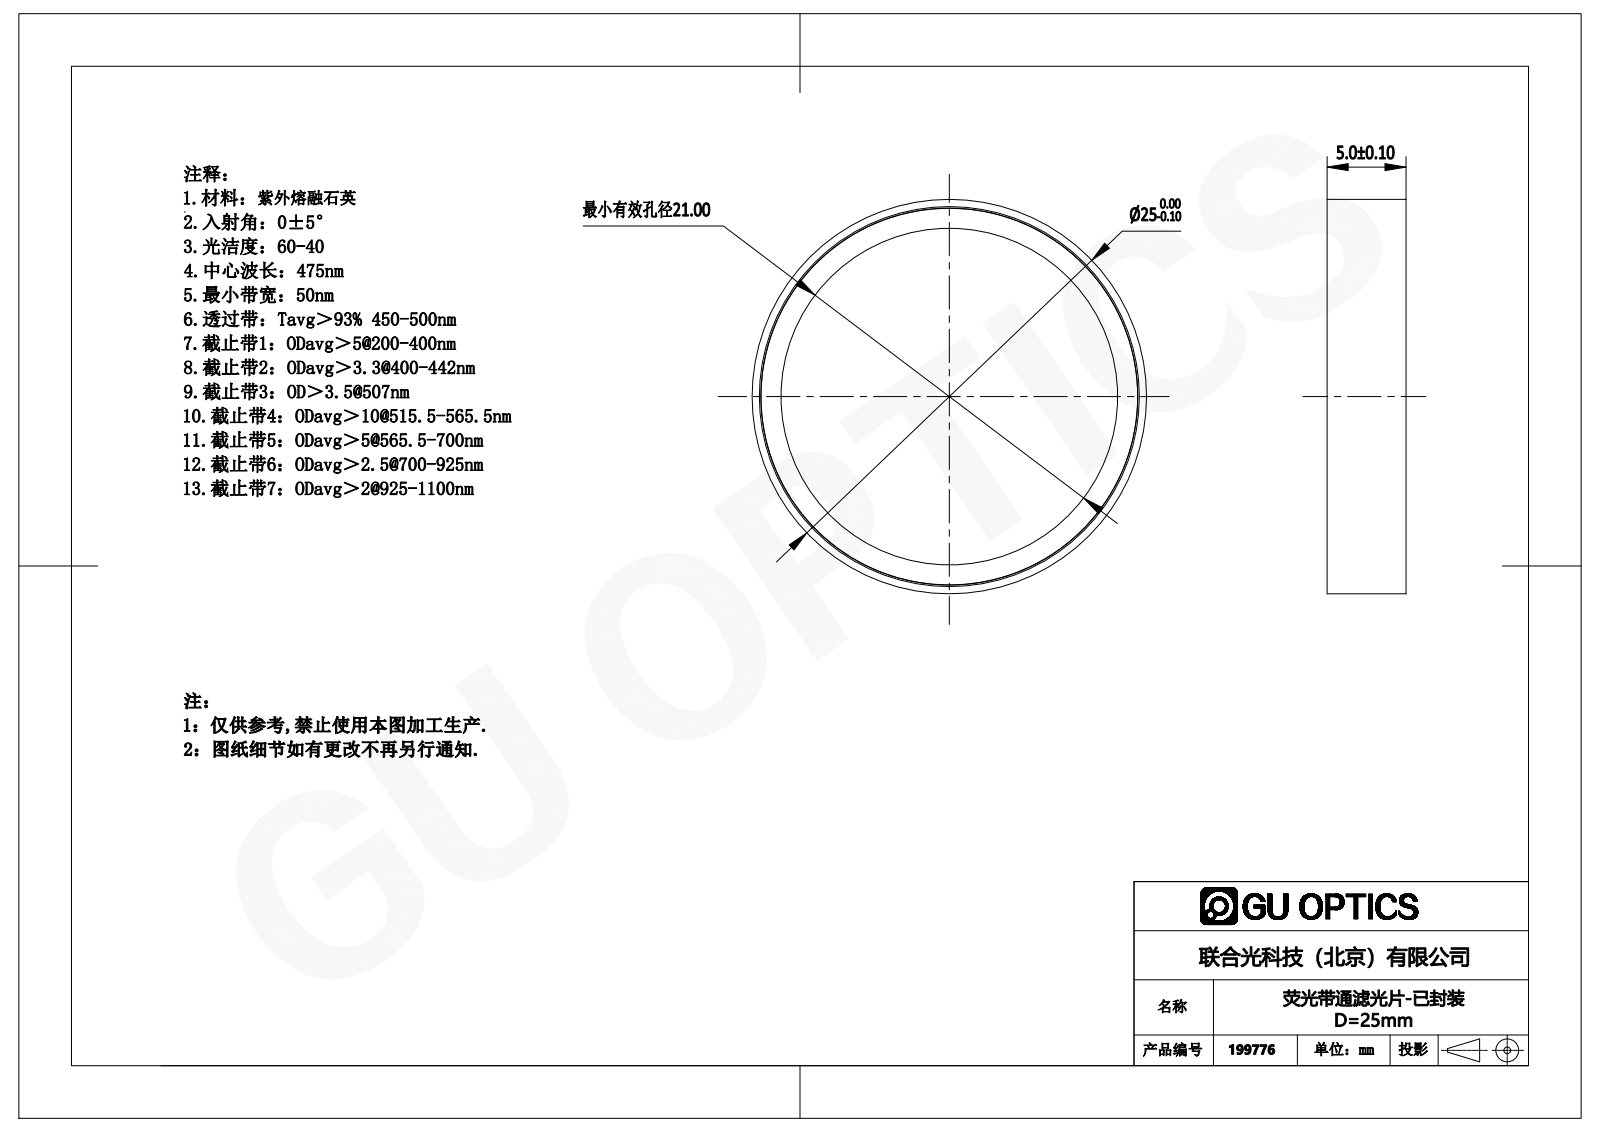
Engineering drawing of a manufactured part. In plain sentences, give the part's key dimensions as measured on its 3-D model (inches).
The part is named "25mm 5mm". Its 3-D file was written by "SolidWorks 2016 (AUTOMOTIVE_DESIGN)". It is 1 solid with 22 faces: 8 planar, 14 cylindrical and 0 other. Overall it measures 0.984 by 0.984 by 0.197 inches. Its volume is 0.073 cubic inches and its surface area 2.649 square inches. Round holes: 1 of diameter 0.866, 1 of diameter 0.941, 1 of diameter 0.957. Round bosses or shafts: 1 of diameter 0.984, 1 of diameter 0.94. The main face-to-face distances are 0.079, 0.039, 0.118, 0.133, 0.094, 0.015, 0.197, 0.157, 0.064, 0.047.
